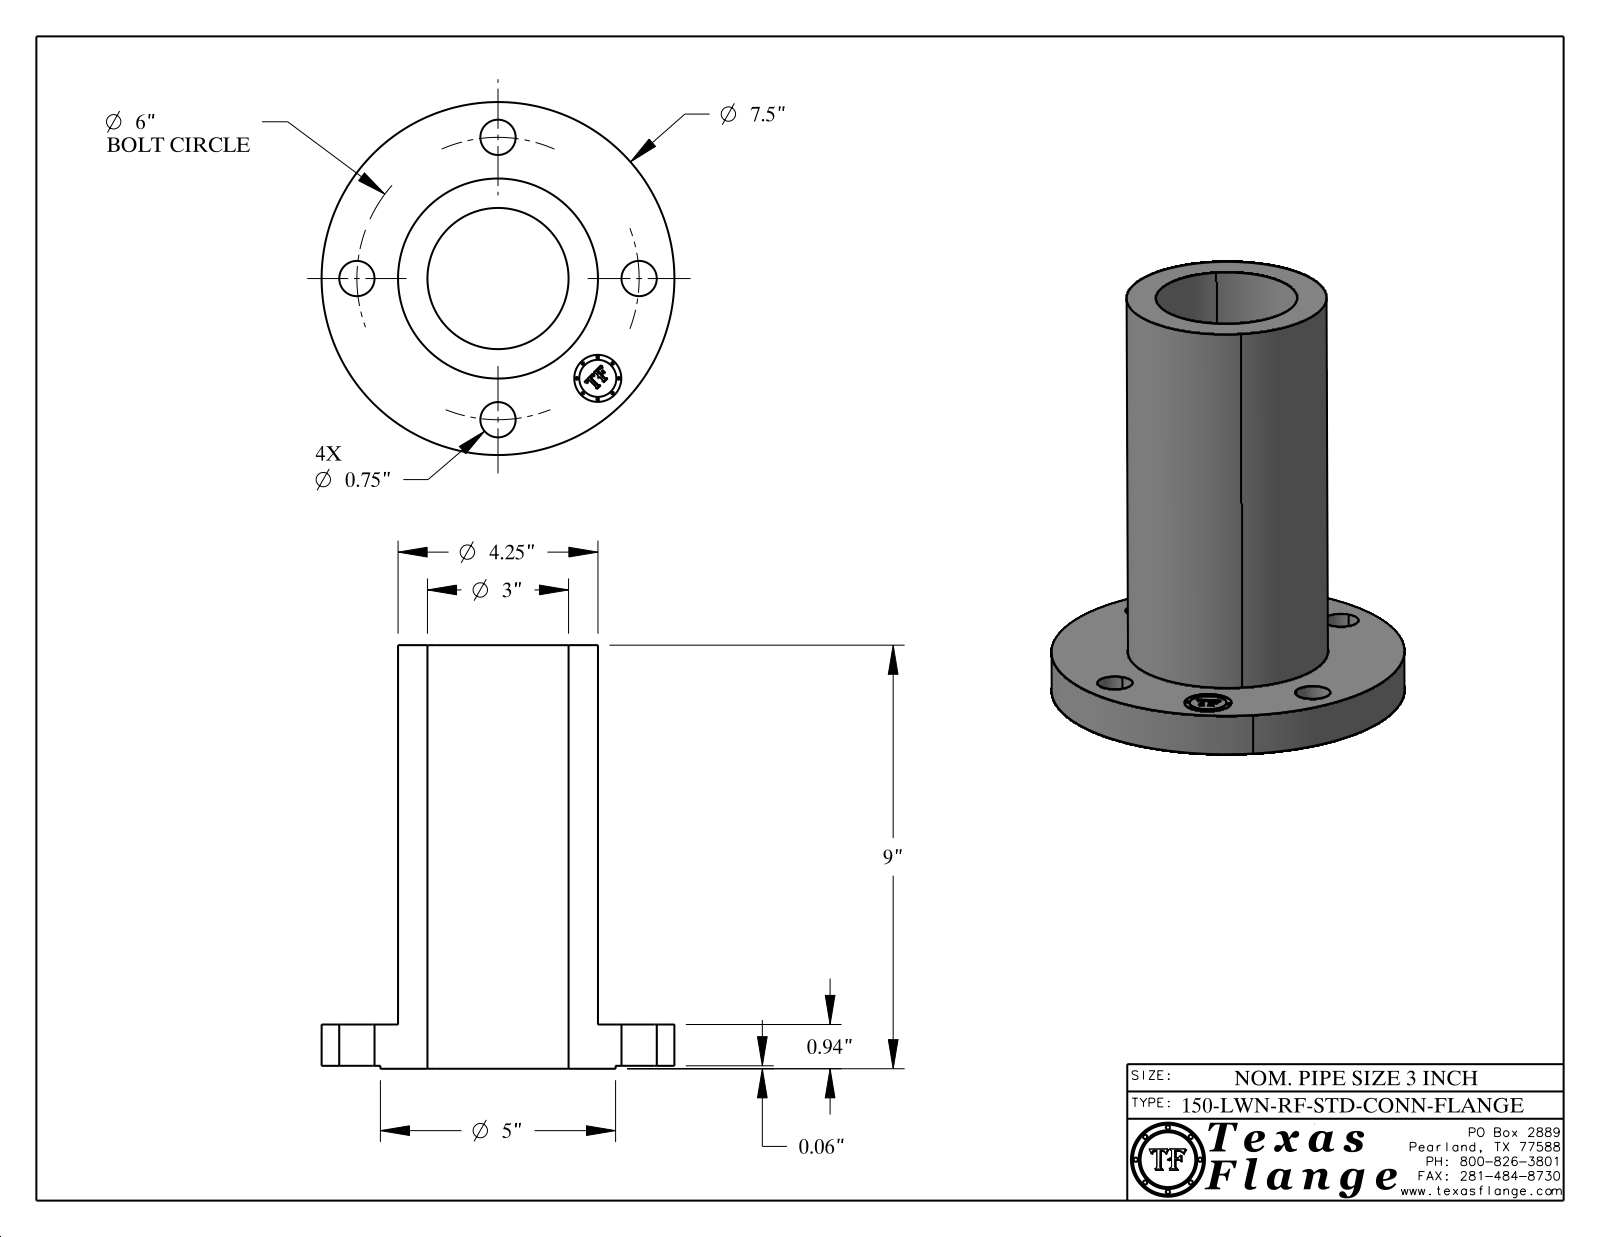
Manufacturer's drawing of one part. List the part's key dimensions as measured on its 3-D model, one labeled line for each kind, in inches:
Part name (STEP PRODUCT): 3-150-LWN-RF-STD-CONN-FLANGE
STEP written by: CATIA V5 STEP AP214 (AUTOMOTIVE_DESIGN)
Units: inches
Bodies: 1 solid, 405 faces (369 planar, 36 cylindrical, 0 other)
Overall size (bounding box): 9 × 7.5 × 7.5
Volume: 89.17 in³ · Surface area: 293.1 in²
Round holes (diameter × count): ⌀0.75 ×4, ⌀1 ×1, ⌀3 ×1
Round bosses / shafts (diameter × count): ⌀0.061 ×8, ⌀7.5 ×1, ⌀5 ×1, ⌀4.25 ×1, ⌀0.788 ×1
Main face-to-face distances: 0.878, 0.063, 0.94, 9, 8.937, 8.06, 0.935, 0.872, 8.065, 0.298
Hole centre spacings: 3, 4.243, 2.296, 5.543, 6
